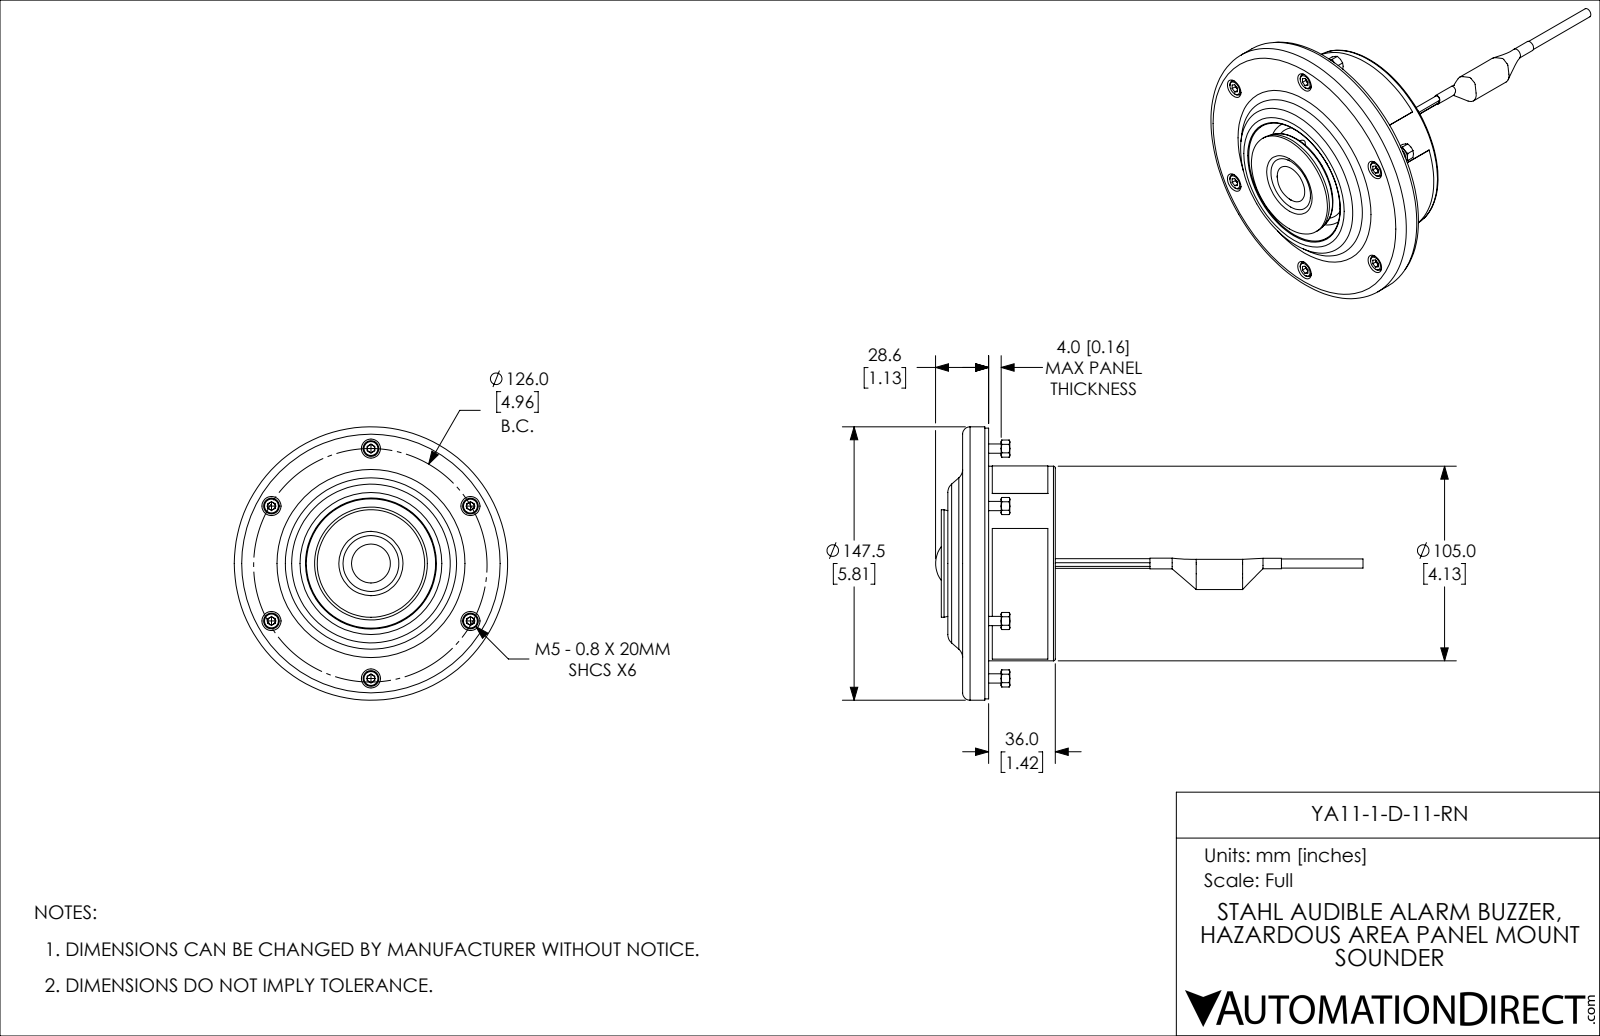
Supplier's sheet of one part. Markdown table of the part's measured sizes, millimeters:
| quantity | value |
| --- | --- |
| part name | YA11-1-D-11-RN |
| STEP written by | SolidWorks 2019 (CONFIG_CONTROL_DESIGN) |
| units | millimeters |
| bodies | 23 solids, 589 faces (207 planar, 168 cylindrical, 214 other) |
| overall size | 147.5 × 147.5 × 127.7 |
| volume | 340 096 mm³ |
| surface area | 141 545 mm² |
| round holes (diameter × count) | 4.2 × 6, 5 × 6, 5.3 × 6, 5.5 × 6, 10.3 × 6, 4 × 3, 6.5 × 3, 2.5 × 2, 7 × 1, 9.5 × 1, 10 × 1, 47 × 1 |
| round bosses / shafts (diameter × count) | 8.5 × 6, 147.5 × 1, 146 × 1, 97 × 1, 94.6 × 1, 58 × 1, 13 × 1 |
| partial cylindrical surfaces (radius × count) | 2 × 4, 1 × 2, 1.3 × 2, 1.6 × 2, 52.6 × 1, 52.7 × 1 |
| main face-to-face distances | 31.5, 2, 29.5, 30, 1.5, 28, 12, 43.5, 42, 14 |
| hole center spacings | 62, 54.68, 53.84, 74.49, 79.04, 107.39, 20.64, 41.36 |
